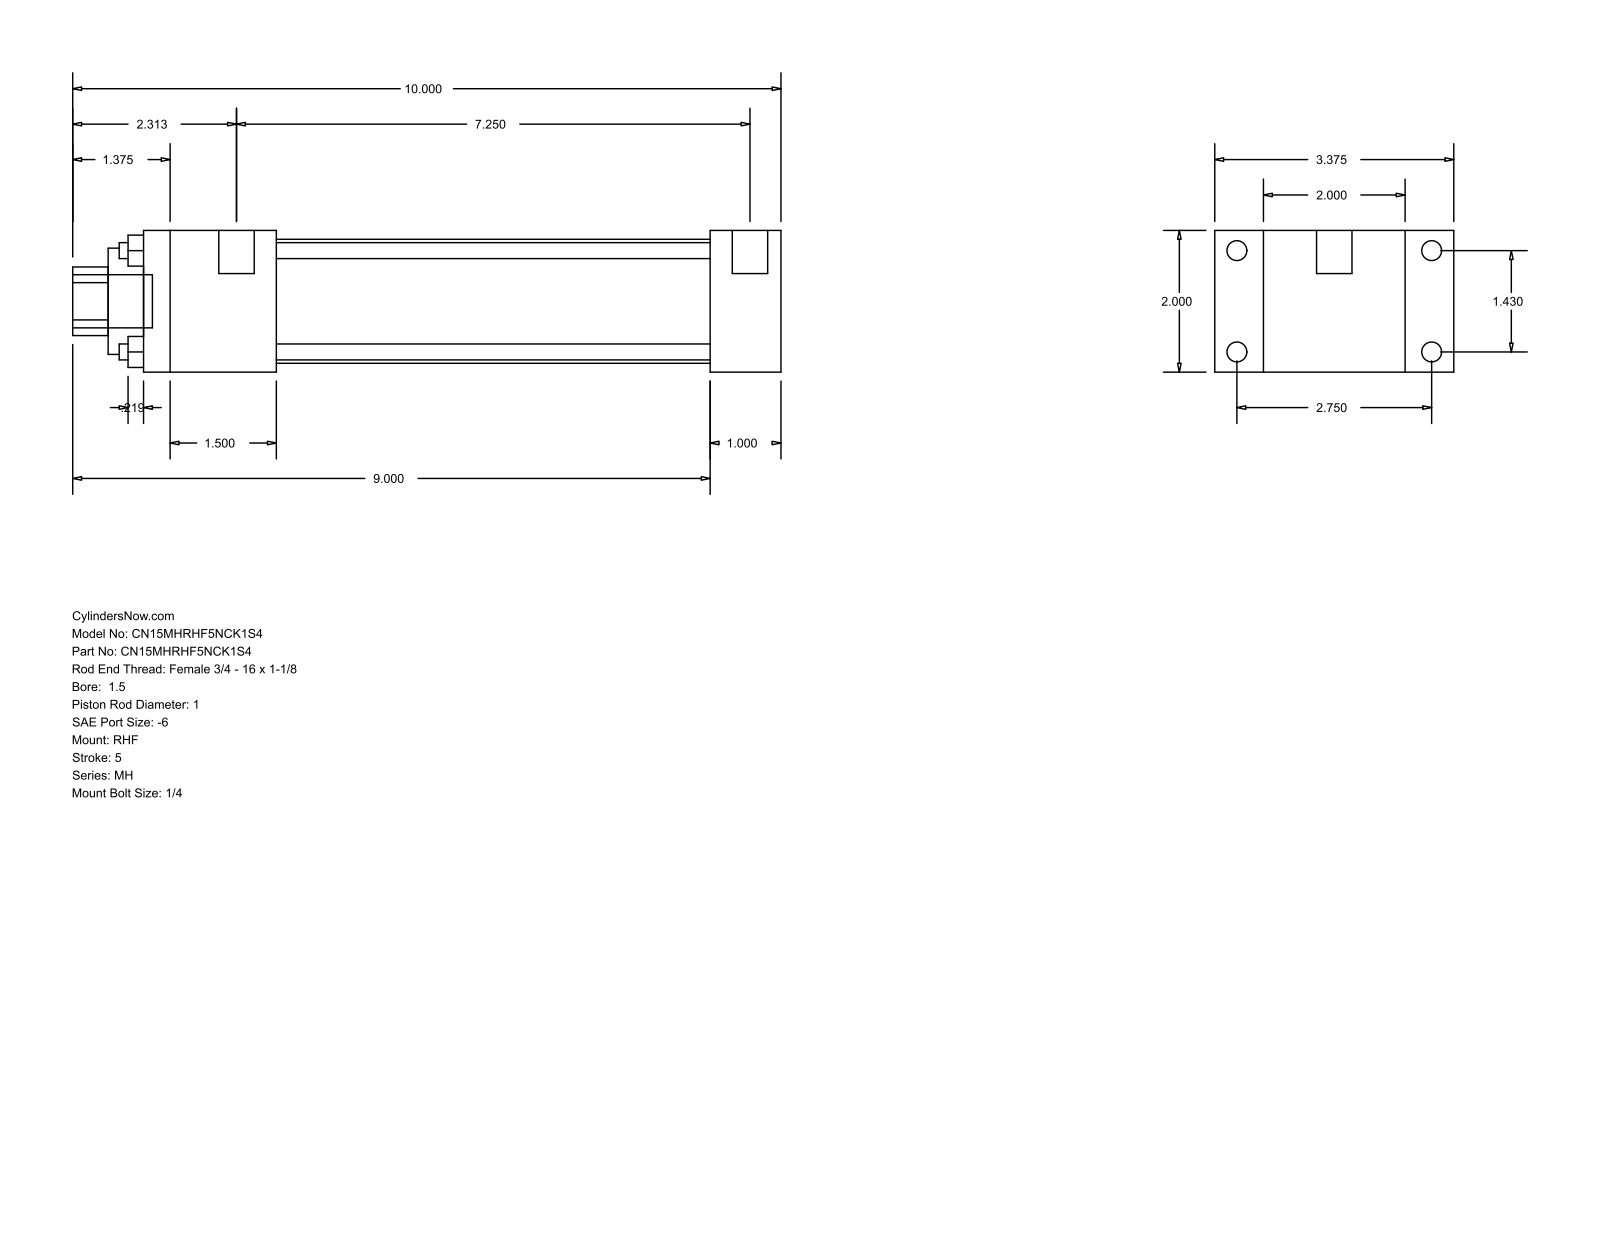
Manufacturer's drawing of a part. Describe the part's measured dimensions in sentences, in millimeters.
The part is named "MH_RHF__0150_1". Its 3-D file was written by "GSSL Pune (CONFIG_CONTROL_DESIGN)". It is 0 solids with 88 faces: 60 planar, 28 cylindrical and 0 other. Overall it measures 254 by 85.72 by 50.8 millimeters. Round holes: 4 of diameter 5.71, 1 of diameter 25.4, 1 of diameter 38.1, 1 of diameter 44.45. Round bosses or shafts: 4 of diameter 7.14, 4 of diameter 5.56, 2 of diameter 12.7, 1 of diameter 19.05. Partial cylindrical surfaces (rounded edges, fillets, slot ends): 1 of radius 12.29. The main face-to-face distances are 50.8, 25.4, 17.46, 68.26, 85.72, 228.6, 203.2, 47.63, 155.57, 180.97. The hole center spacings are 25.68, 36.32, 51.36.
